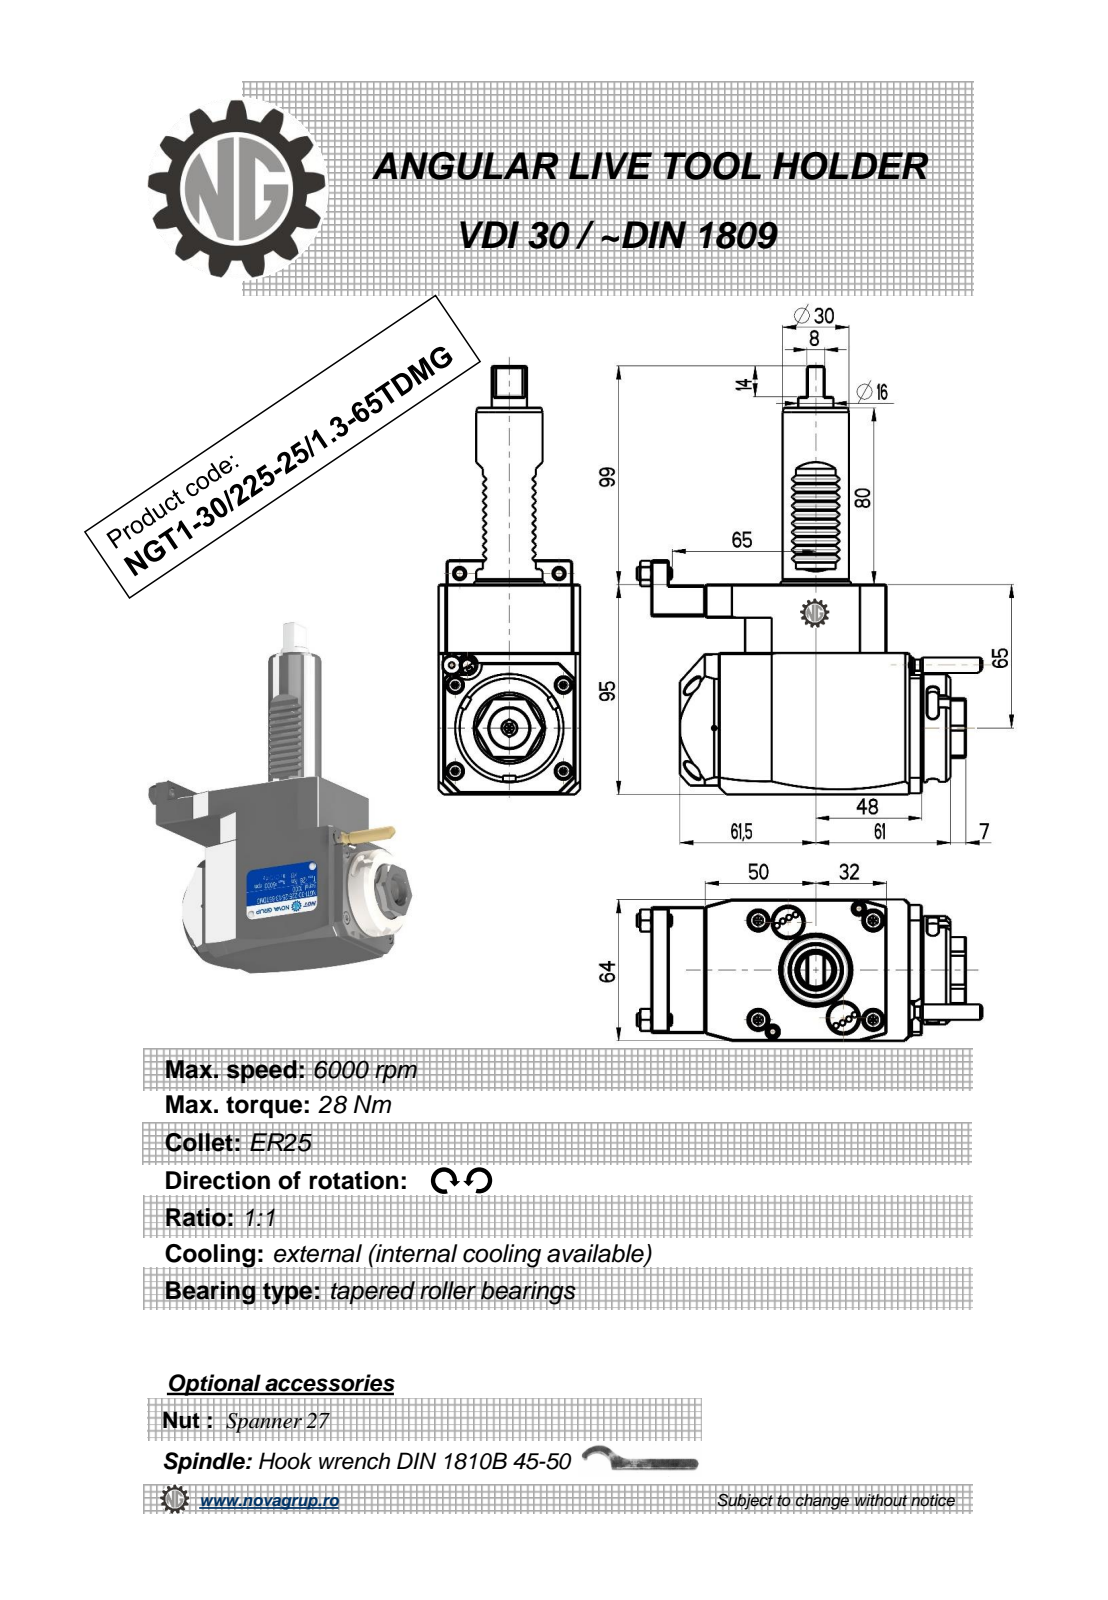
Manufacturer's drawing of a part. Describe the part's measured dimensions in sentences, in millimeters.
The part is named "NGT1_30_225_25_1_3_65TDMG". Its 3-D file was written by "PRO/ENGINEER BY PARAMETRIC TECHNOLOGY CORPORATION, 2010280 (CONFIG_CONTROL_DESIGN)". It is 1 solid with 406 faces: 228 planar, 82 cylindrical and 96 other. Overall it measures 194 by 156.38 by 64 millimeters. Its volume is 649 600 cubic millimeters and its surface area 61 903 square millimeters. Round holes: 1 of diameter 2.5, 1 of diameter 3, 1 of diameter 18. Round bosses or shafts: 2 of diameter 6, 1 of diameter 49, 1 of diameter 42, 1 of diameter 30, 1 of diameter 15.9, 1 of diameter 8, 1 of diameter 7, 1 of diameter 5. Partial cylindrical surfaces (rounded edges, fillets, slot ends): 20 of radius 0.3, 10 of radius 0.31, 6 of radius 2.5, 2 of radius 0.8, 2 of radius 180, 1 of radius 4.5, 1 of radius 15, 1 of radius 21.5. The main face-to-face distances are 64, 95, 16, 0.5, 13, 80, 122.5, 14.5, 16.5, 80.5. The hole center spacings are 34.25.
